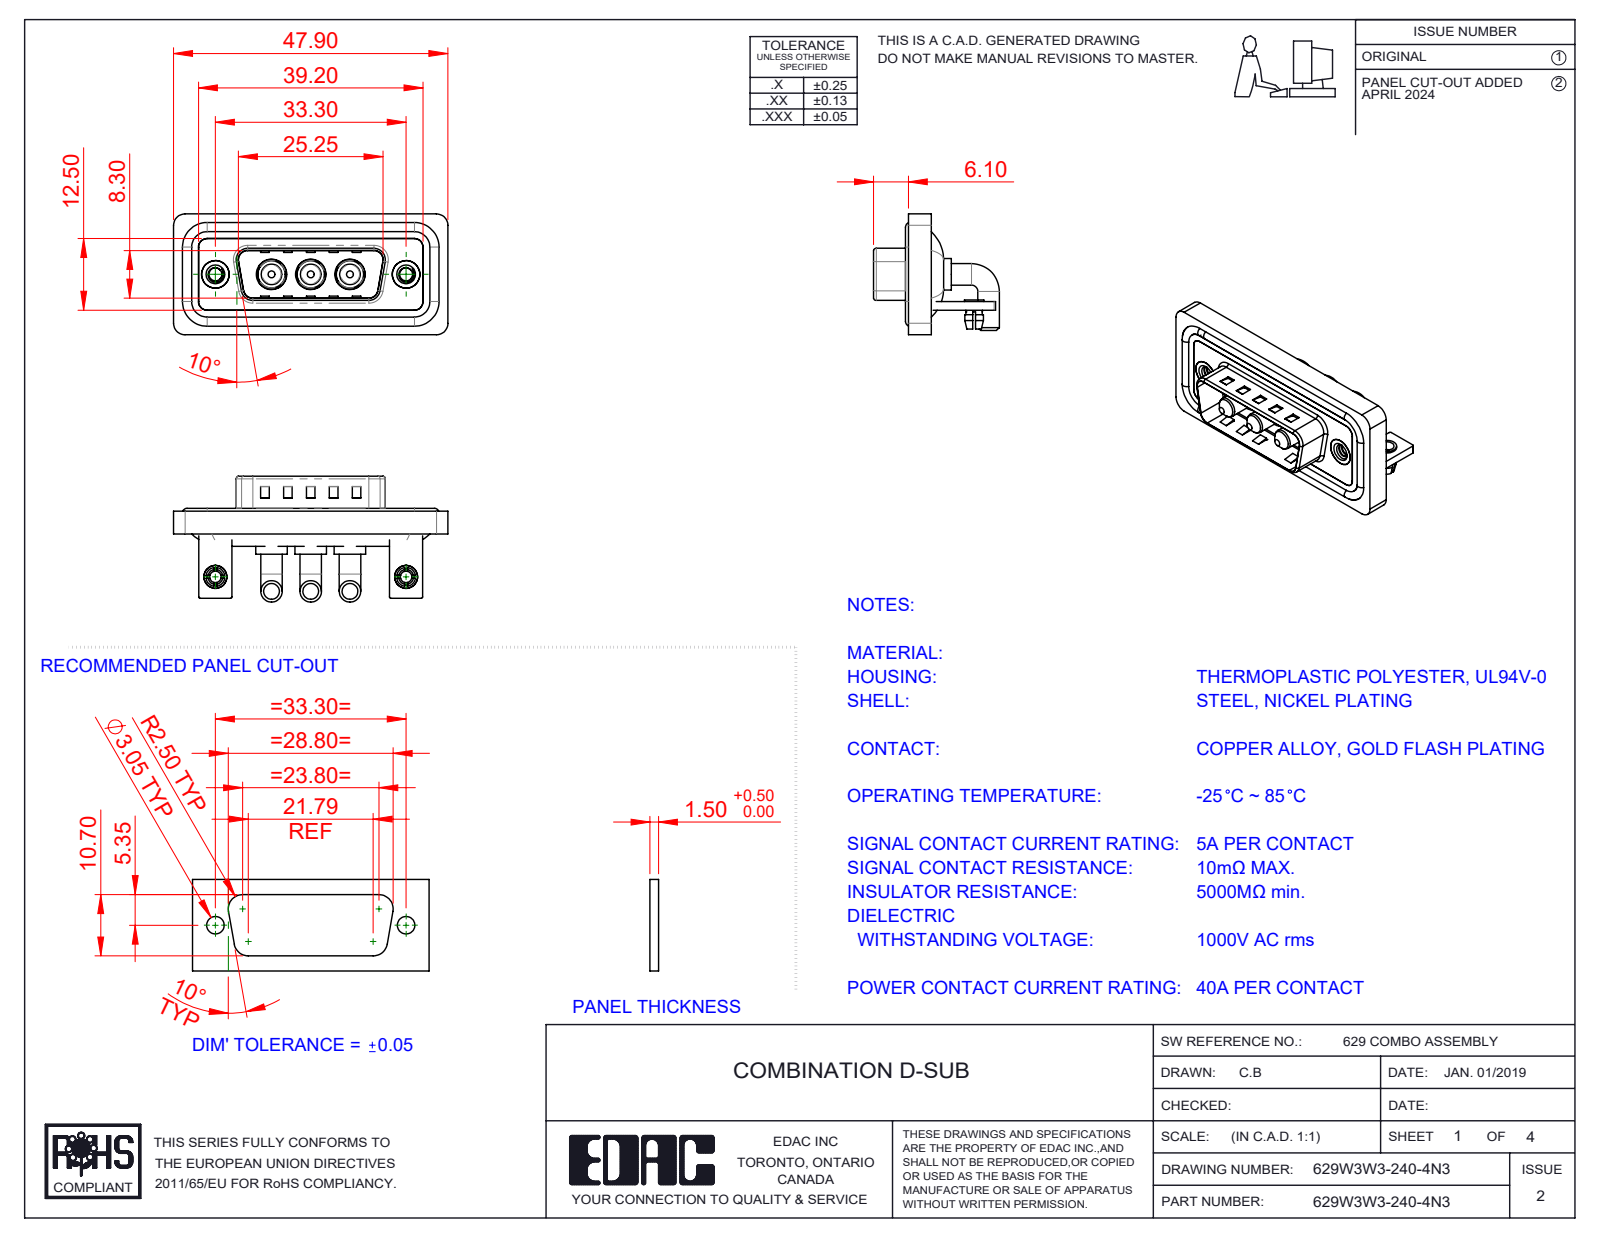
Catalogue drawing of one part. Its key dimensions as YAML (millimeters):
part_name: "Power Pin_40A RA; 629Combo Stabilizer Bracket; 629Combo Shell Rear_15 Contacts; 629Combo Shell Front_15 Contacts (+5 more)"
step_written_by: "SolidWorks 2023 (CONFIG_CONTROL_DESIGN)"
units: millimeters
bodies: {solids: 17, faces: 708, planar: 275, cylindrical: 297, other: 136}
overall_size: [47.9, 21.98, 21.1]
volume: 6311
surface_area: 9965
round_holes:
  - {diameter: 4.85, count: 3}
  - {diameter: 5.3, count: 3}
  - {diameter: 2, count: 2}
  - {diameter: 2.26, count: 2}
  - {diameter: 2.5, count: 2}
  - {diameter: 3.2, count: 2}
  - {diameter: 4, count: 2}
  - {diameter: 4.8, count: 2}
  - {diameter: 5, count: 2}
round_bosses_or_shafts:
  - {diameter: 3.75, count: 6}
  - {diameter: 1.6, count: 4}
  - {diameter: 5.5, count: 3}
  - {diameter: 5.2, count: 3}
  - {diameter: 4.75, count: 3}
  - {diameter: 3.6, count: 3}
  - {diameter: 4.9, count: 2}
  - {diameter: 4, count: 2}
partial_cylinders:
  - {radius: 2, count: 21}
  - {radius: 1.5, count: 18}
  - {radius: 0.25, count: 16}
  - {radius: 0.5, count: 9}
  - {radius: 1.6, count: 8}
  - {radius: 0.6, count: 4}
  - {radius: 0.65, count: 4}
  - {radius: 0.9, count: 4}
face_to_face_distances: [0.4, 1.5, 0.8, 2.9, 1.1, 2.1, 3.7, 1.6, 1.2, 4.5]
hole_center_spacings: [6.85, 9.8, 16.65, 23.5, 33.3, 13.7]
